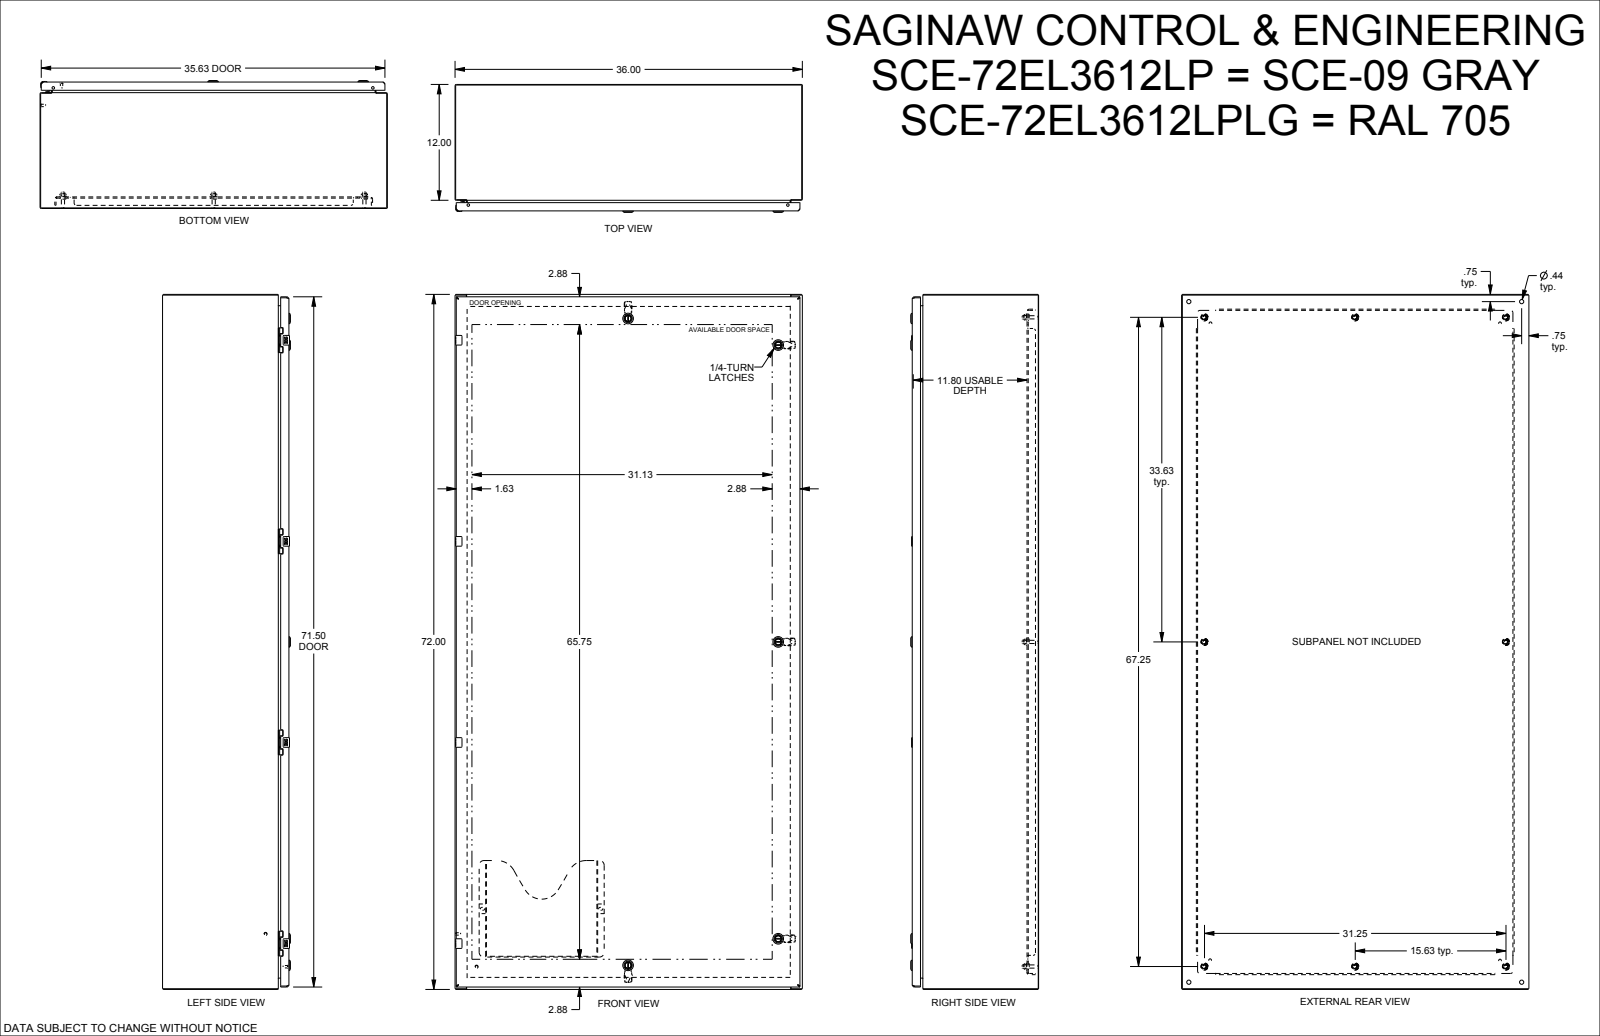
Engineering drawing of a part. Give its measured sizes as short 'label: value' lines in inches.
name: SCE-72EL3612LPLG
written by: SolidWorks 2019 (CONFIG_CONTROL_DESIGN)
unit: in
bodies: 0 solids, 5207 faces (2557 planar, 1466 cylindrical, 1184 other)
size: 72 × 36 × 13.256
holes: 8× ⌀0.172, 8× ⌀0.205, 8× ⌀0.244, 8× ⌀0.266, 8× ⌀0.367, 8× ⌀0.375, 8× ⌀0.5, 5× ⌀0.197, 5× ⌀0.315, 5× ⌀0.394, 5× ⌀0.634, 4× ⌀0.04
bosses: 12× ⌀0.17, 8× ⌀0.366, 8× ⌀0.332, 8× ⌀0.25, 8× ⌀0.24, 5× ⌀1.102, 5× ⌀0.866, 5× ⌀0.802
rounds: 136× R0.012, 52× R0.01, 52× R0.02, 40× R0.015, 25× R0.03, 20× R0.025, 20× R0.1, 20× R0.157
face distances: 0.075, 0.104, 12.92, 12.995, 13.099, 13.024, 1.125, 11.795, 1, 11.92
hole spacings: 20.833, 41.667, 20.833, 62.5, 0.493, 0.05, 0.494, 0.986
